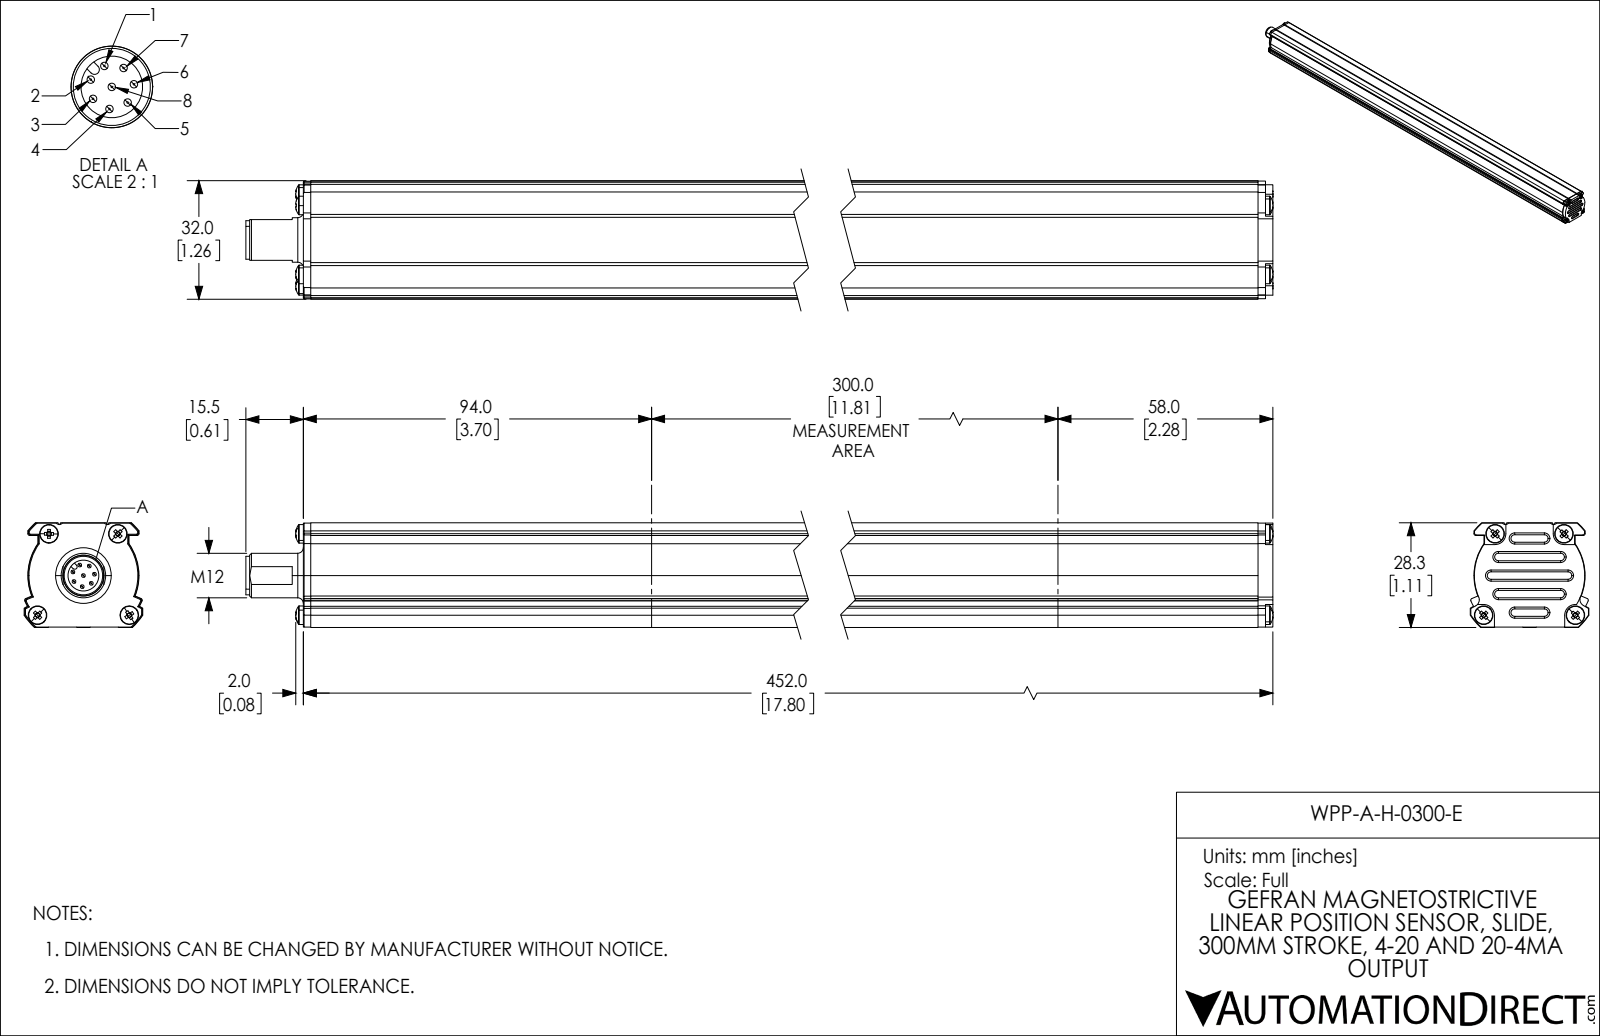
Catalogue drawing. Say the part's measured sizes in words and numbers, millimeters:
The part is named "WPP-A-H-0300-E". Its 3-D file was written by "SolidWorks 2021 (CONFIG_CONTROL_DESIGN)". It is 20 solids with 605 faces: 301 planar, 131 cylindrical and 173 other. Overall it measures 467.55 by 32 by 28.25 millimeters. Its volume is 360 774 cubic millimeters and its surface area 76 528 square millimeters. Round holes: 5 of diameter 2.6, 4 of diameter 2.3, 1 of diameter 7, 1 of diameter 8.3, 1 of diameter 9.4. Round bosses or shafts: 8 of diameter 1, 4 of diameter 5, 1 of diameter 12, 1 of diameter 10.4, 1 of diameter 9.55, 1 of diameter 8. Partial cylindrical surfaces (rounded edges, fillets, slot ends): 8 of radius 0.5, 4 of radius 2.9, 2 of radius 0.4, 2 of radius 1, 2 of radius 1.85, 1 of radius 0.65, 1 of radius 2, 1 of radius 14.9. The main face-to-face distances are 28, 28.25, 24.8, 24.55, 3.45, 3.7, 28.3, 446, 2, 24.6. The hole center spacings are 16.36, 14.6, 22.17, 30.85, 18.6, 22.16, 24.75, 24.76.
